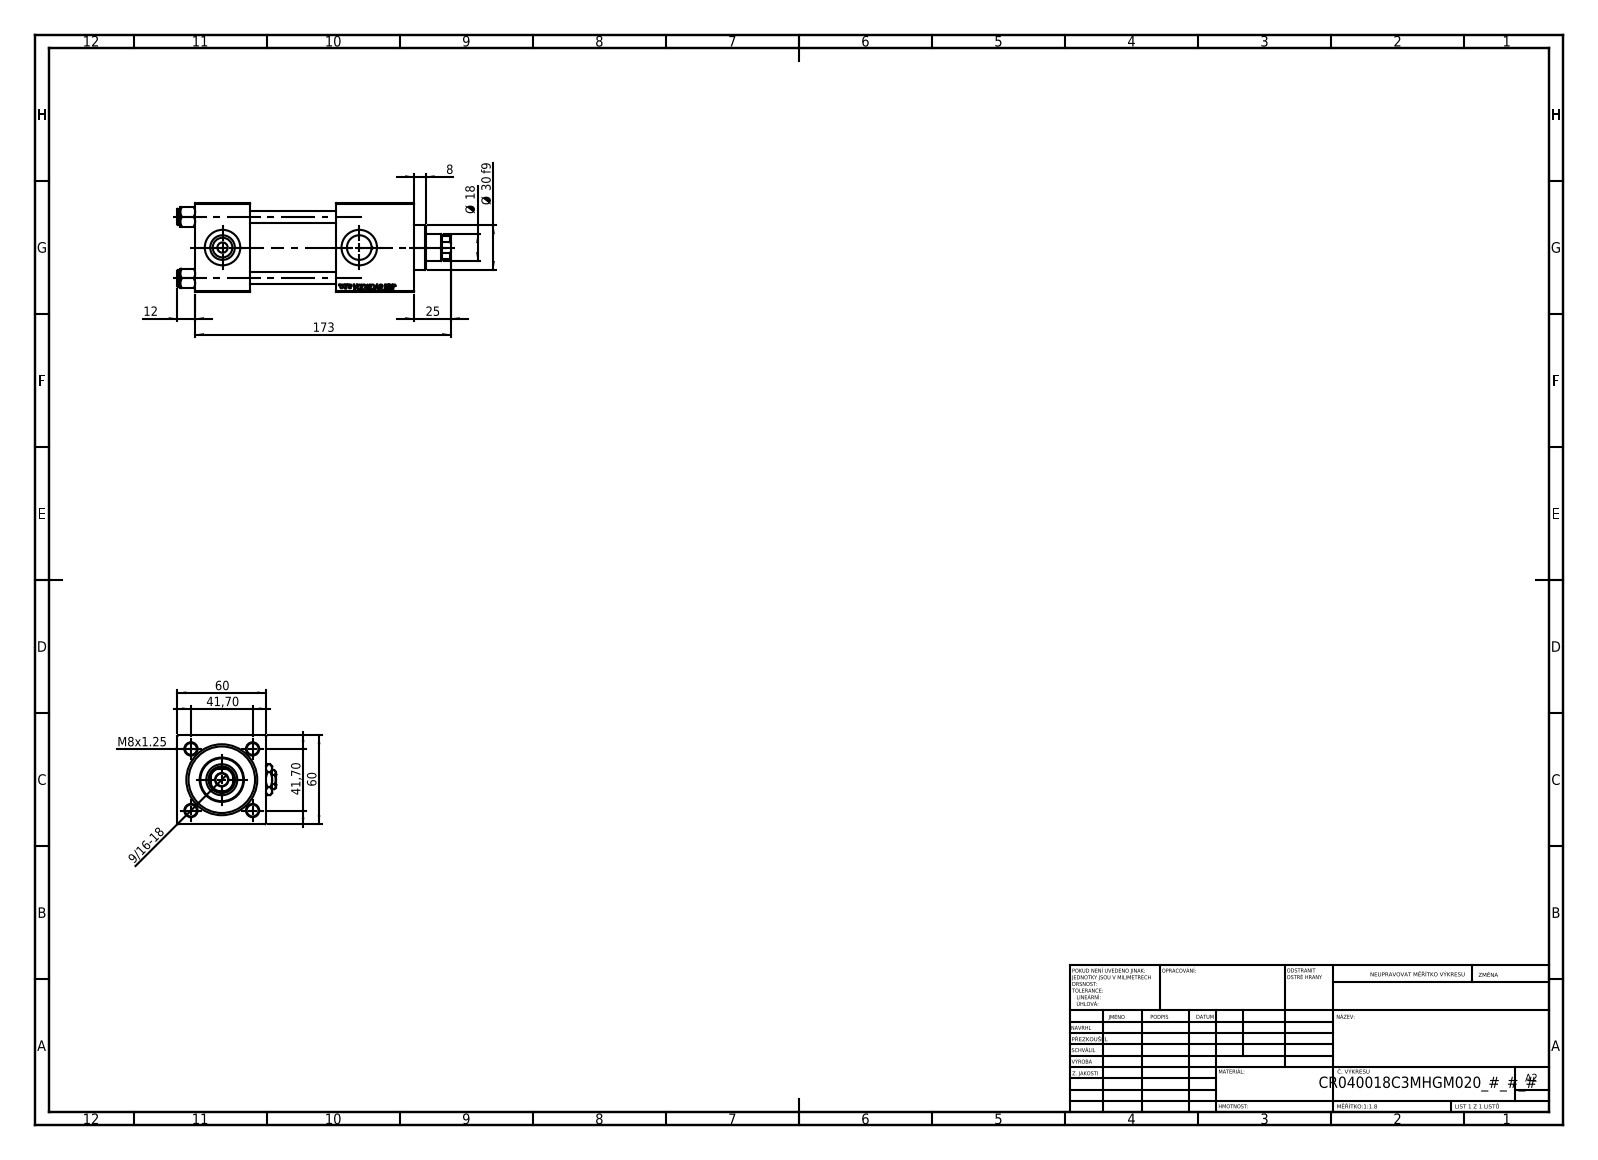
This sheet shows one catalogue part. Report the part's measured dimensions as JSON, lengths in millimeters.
{"part_name": "V215_VC_A; V215CR_VCP_C; NUT_M5_C; V215CR_C_TYCINKA (+2 more)", "step_written_by": "SolidWorks 2019 (CONFIG_CONTROL_DESIGN)", "units": "millimeters", "bodies": {"solids": 13, "faces": 1250, "planar": 574, "cylindrical": 98, "other": 578}, "overall_size": [185, 67, 60], "volume_mm3": 399322, "surface_area_mm2": 108248, "round_holes": [[8, 4], [7, 2], [16.66, 2], [24, 2], [8.5, 1], [18, 1], [21, 1], [31, 1], [40, 1], [45, 1]], "round_bosses_or_shafts": [[11, 4], [46, 1], [30, 1]], "partial_cylinders_radius": [[8.5, 1]], "face_to_face_distances": [60, 37, 53, 148, 111, 58, 95, 119.3, 82.3, 24.3], "hole_center_spacings": [29.49, 41.7, 58.97, 92.5]}
